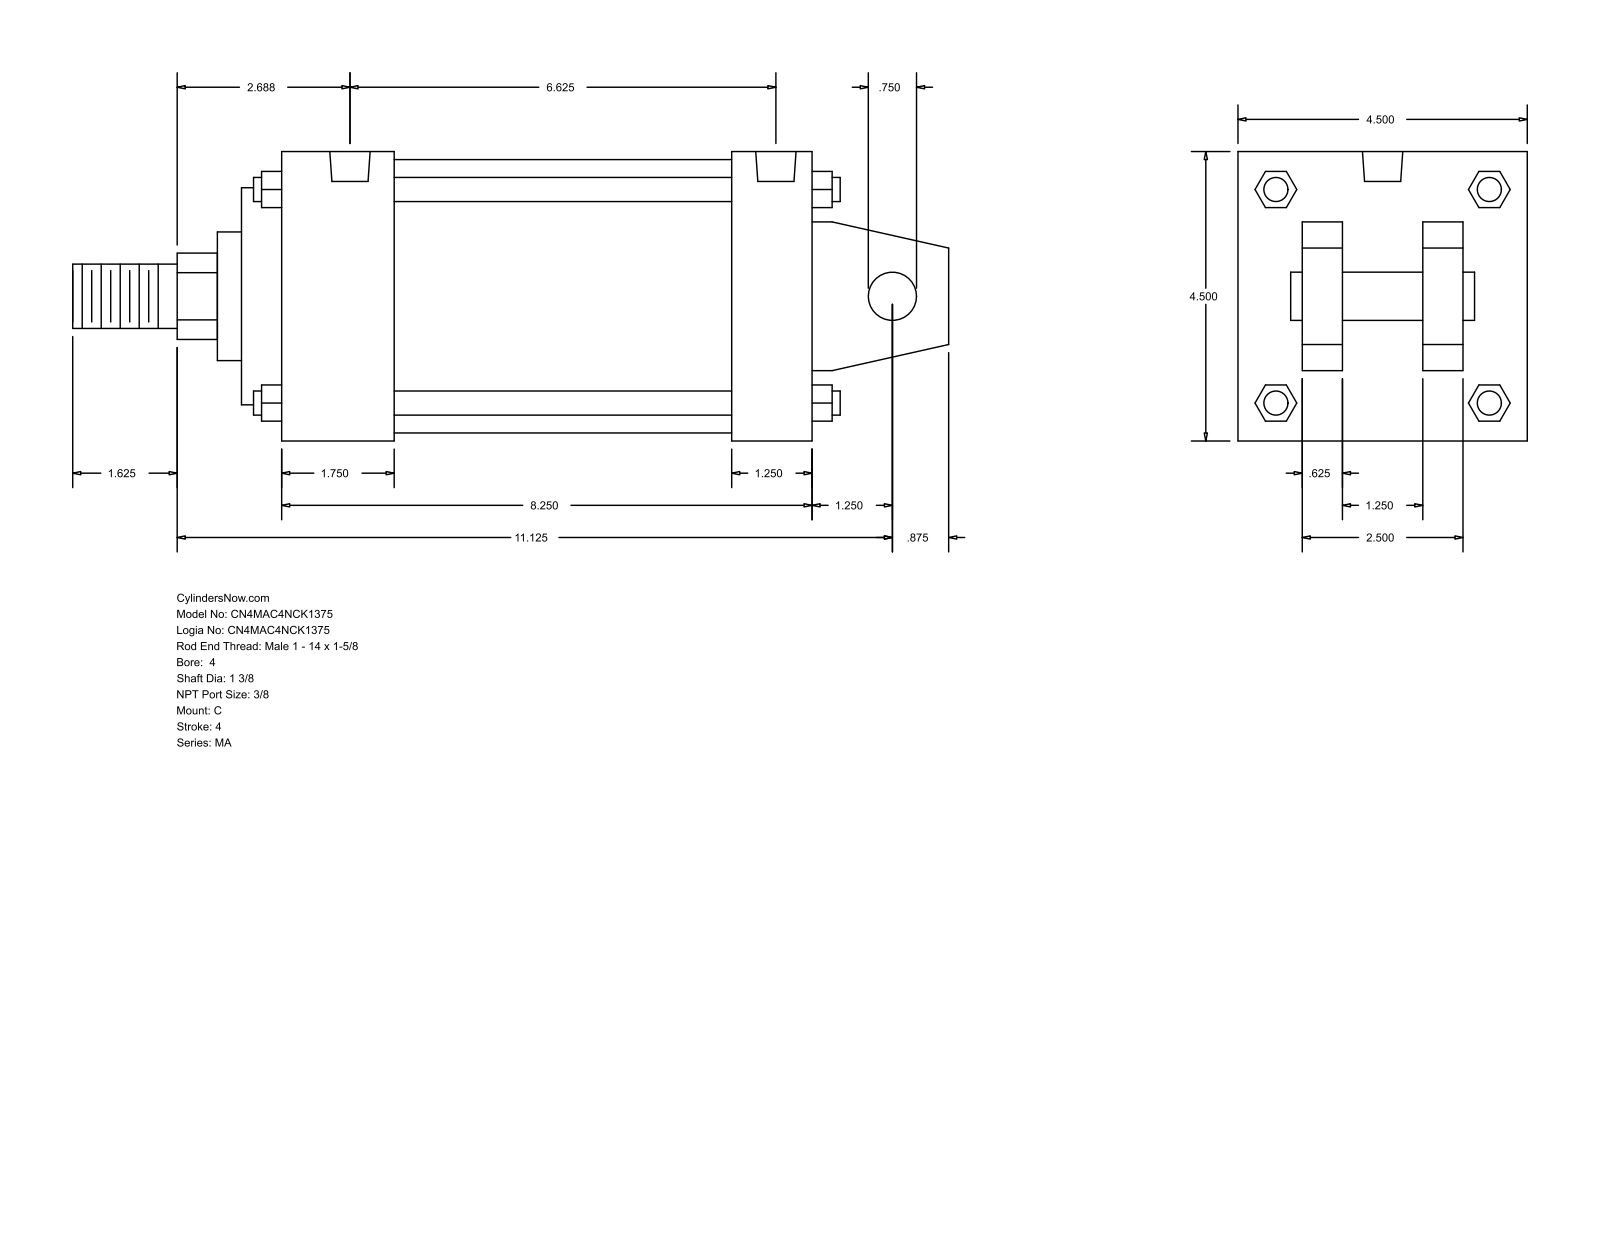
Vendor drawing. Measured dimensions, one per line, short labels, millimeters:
name: MA_C__0400_1.375
written by: GSSL Pune (CONFIG_CONTROL_DESIGN)
unit: mm
bodies: 0 solids, 141 faces (109 planar, 32 cylindrical, 0 other)
size: 346.07 × 114.3 × 114.3
holes: 4× ⌀11.11, 2× ⌀15.93
bosses: 4× ⌀9.53, 1× ⌀107.95, 1× ⌀85.72, 1× ⌀50.8, 1× ⌀34.92, 1× ⌀25.4, 1× ⌀19.05
rounds: 1× R17.06
face distances: 114.3, 15.87, 209.55, 73.03, 41.27, 25.4, 88.9, 47.63, 225.42, 193.67
hole spacings: 158.75, 4.76, 4.77, 163.51, 163.52, 168.28
